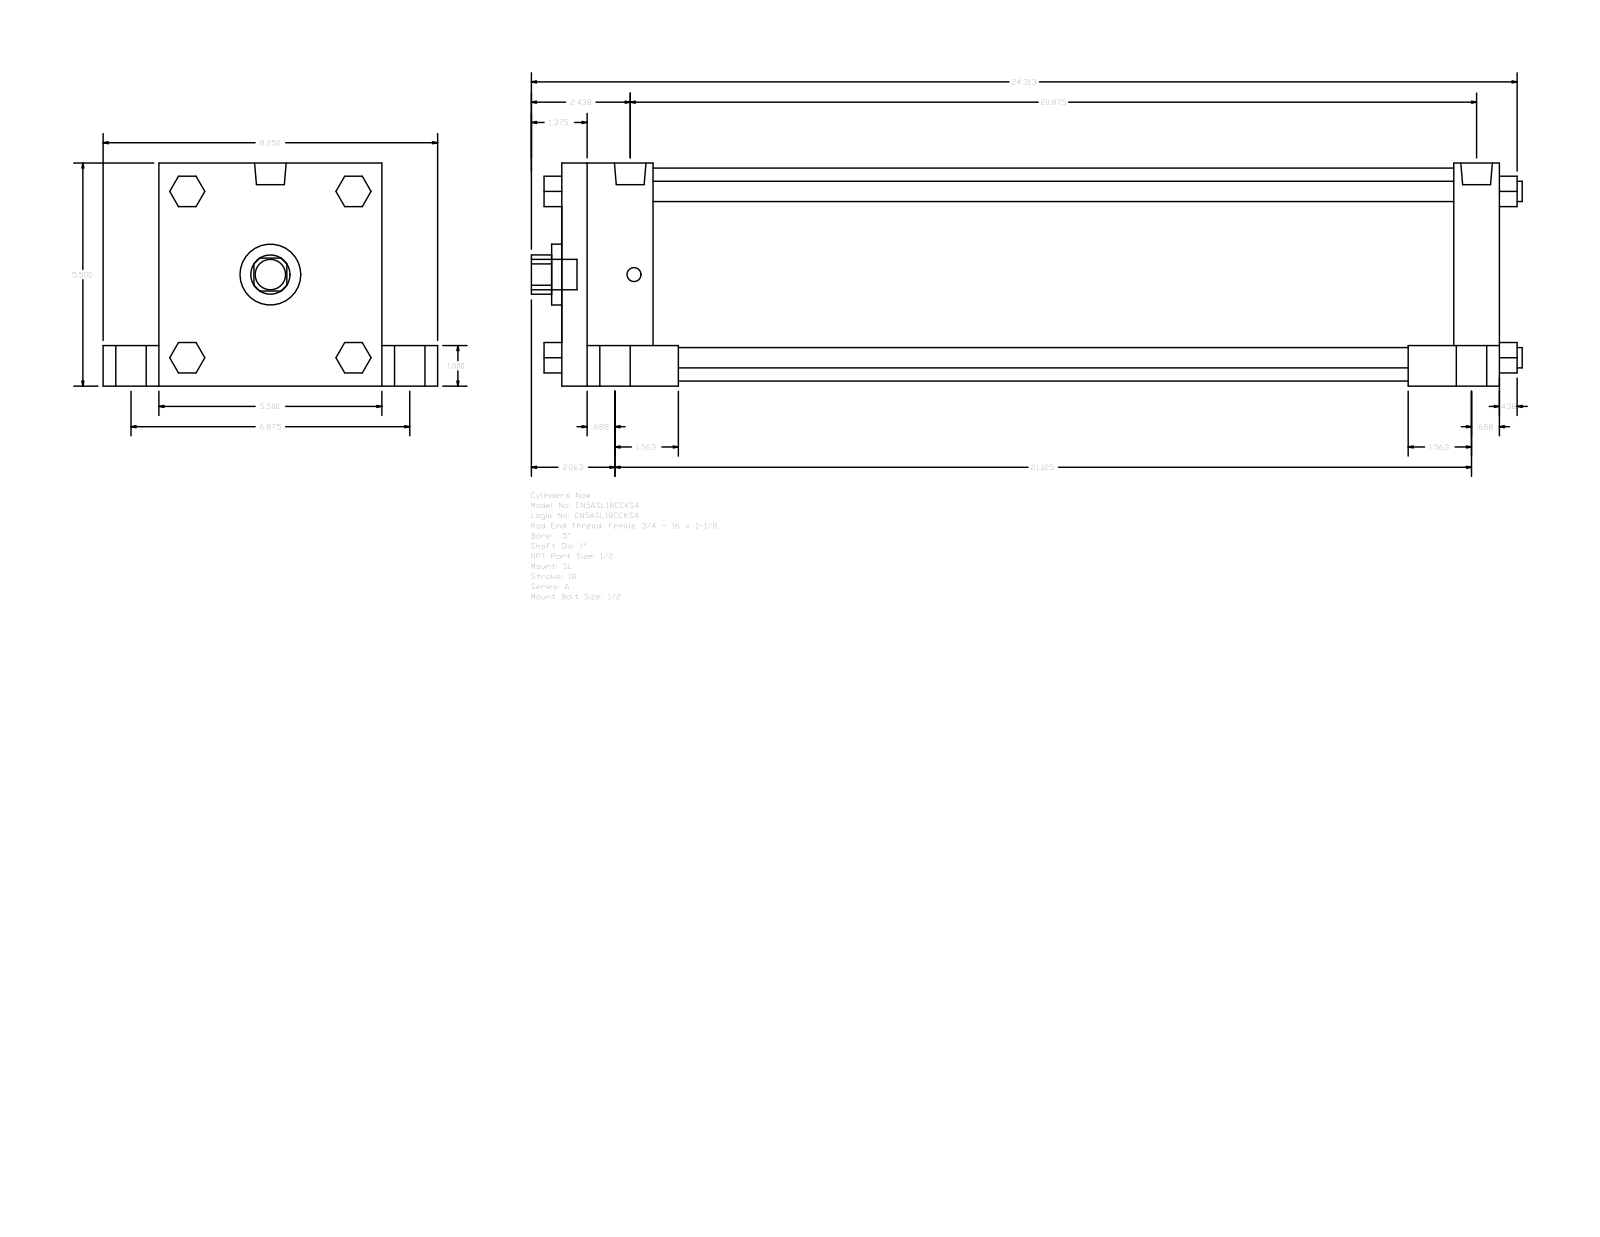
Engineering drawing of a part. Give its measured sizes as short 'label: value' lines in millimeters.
name: A_SL__0500_1
written by: GSSL Pune (CONFIG_CONTROL_DESIGN)
unit: mm
bodies: 0 solids, 150 faces (114 planar, 36 cylindrical, 0 other)
size: 620.71 × 209.55 × 139.7
holes: 1× ⌀25.4, 1× ⌀38.1, 1× ⌀133.35
bosses: 5× ⌀19.05, 4× ⌀25.4, 4× ⌀12.7, 4× ⌀8.73, 2× ⌀19.77
rounds: 1× R12.29
face distances: 139.7, 587.37, 57.15, 530.22, 25.4, 114.3, 34.93, 174.63, 28.57, 558.8
